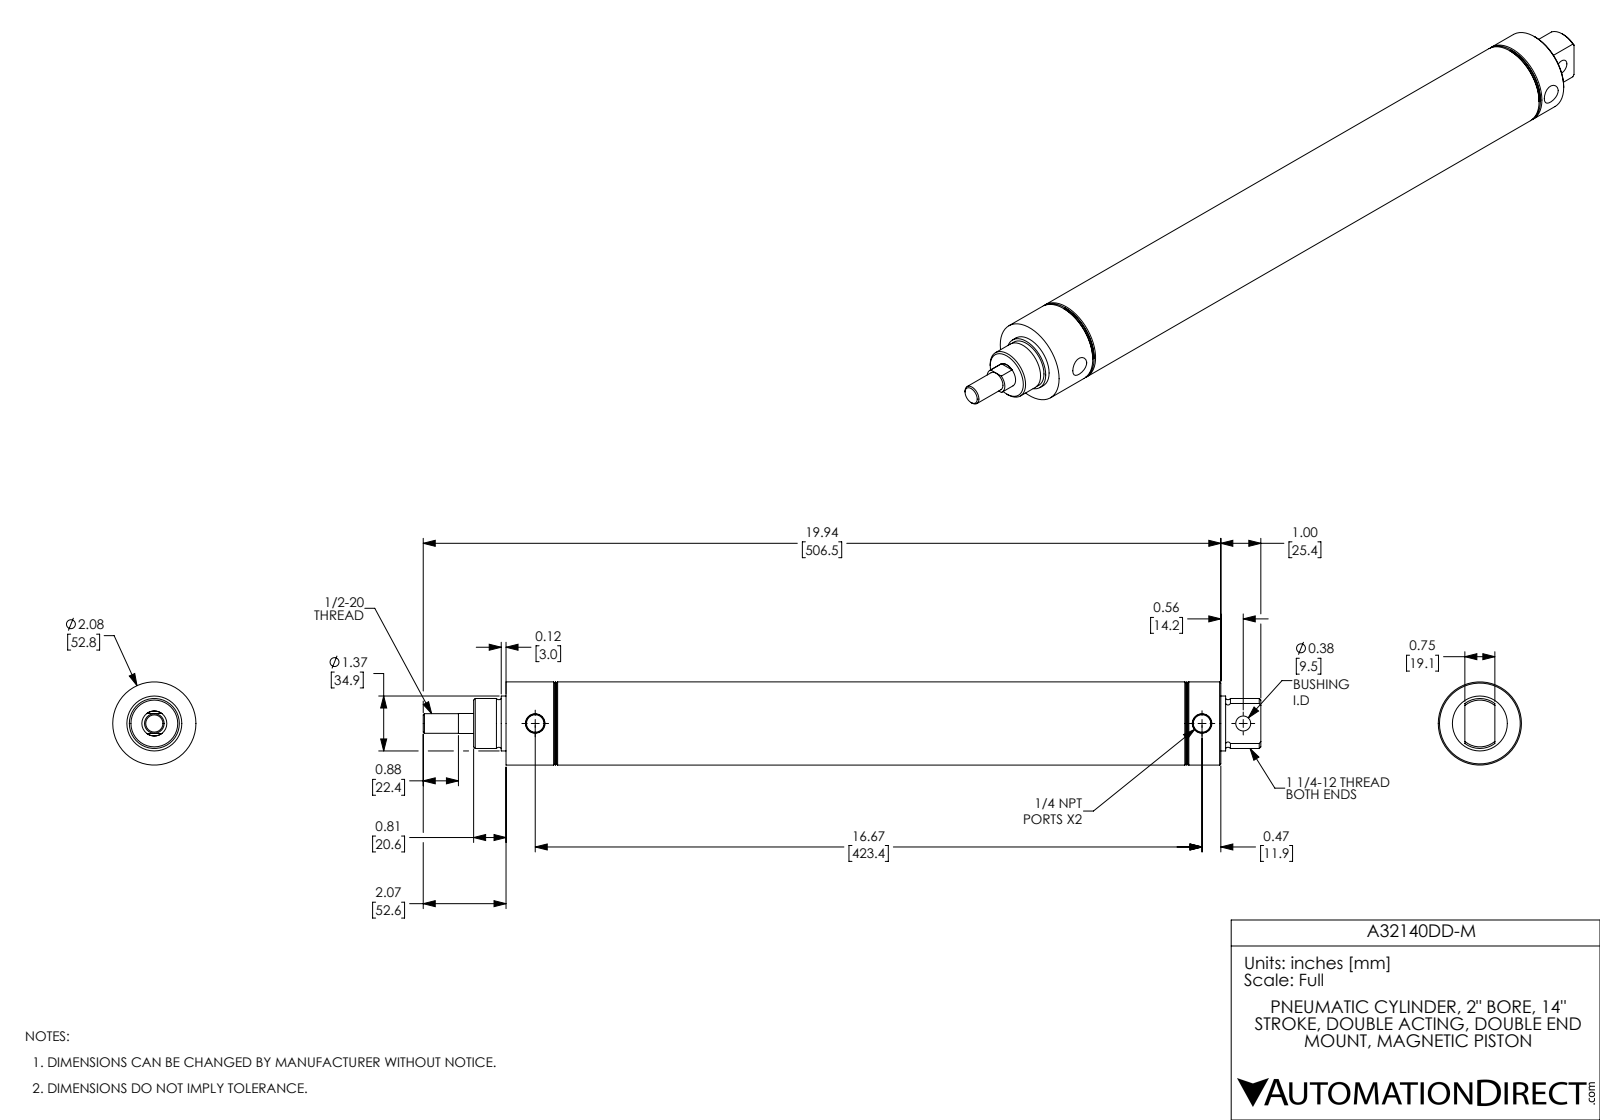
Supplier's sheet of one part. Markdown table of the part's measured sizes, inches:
| quantity | value |
| --- | --- |
| part name | A32140DD-M-MainBody; A32140DD-M; A32140DD-M-Rod |
| STEP written by | SolidWorks 2017 (AUTOMOTIVE_DESIGN) |
| units | inches |
| bodies | 2 solids, 88 faces (20 planar, 30 cylindrical, 38 other) |
| overall size | 20.94 × 2.08 × 2.08 |
| volume | 22.87 in³ |
| surface area | 279.2 in² |
| round holes (diameter × count) | 0.438 × 2, 0.375 × 1, 0.625 × 1, 2 × 1 |
| round bosses / shafts (diameter × count) | 2.08 × 1, 1.373 × 1, 1.25 × 1, 0.491 × 1 |
| main face-to-face distances | 0.5, 14.5, 14, 16.185, 15.685, 1.685, 1.685, 2.185, 16.185, 17.87 |
| hole center spacings | 1.03, 16.67, 17.7 |
